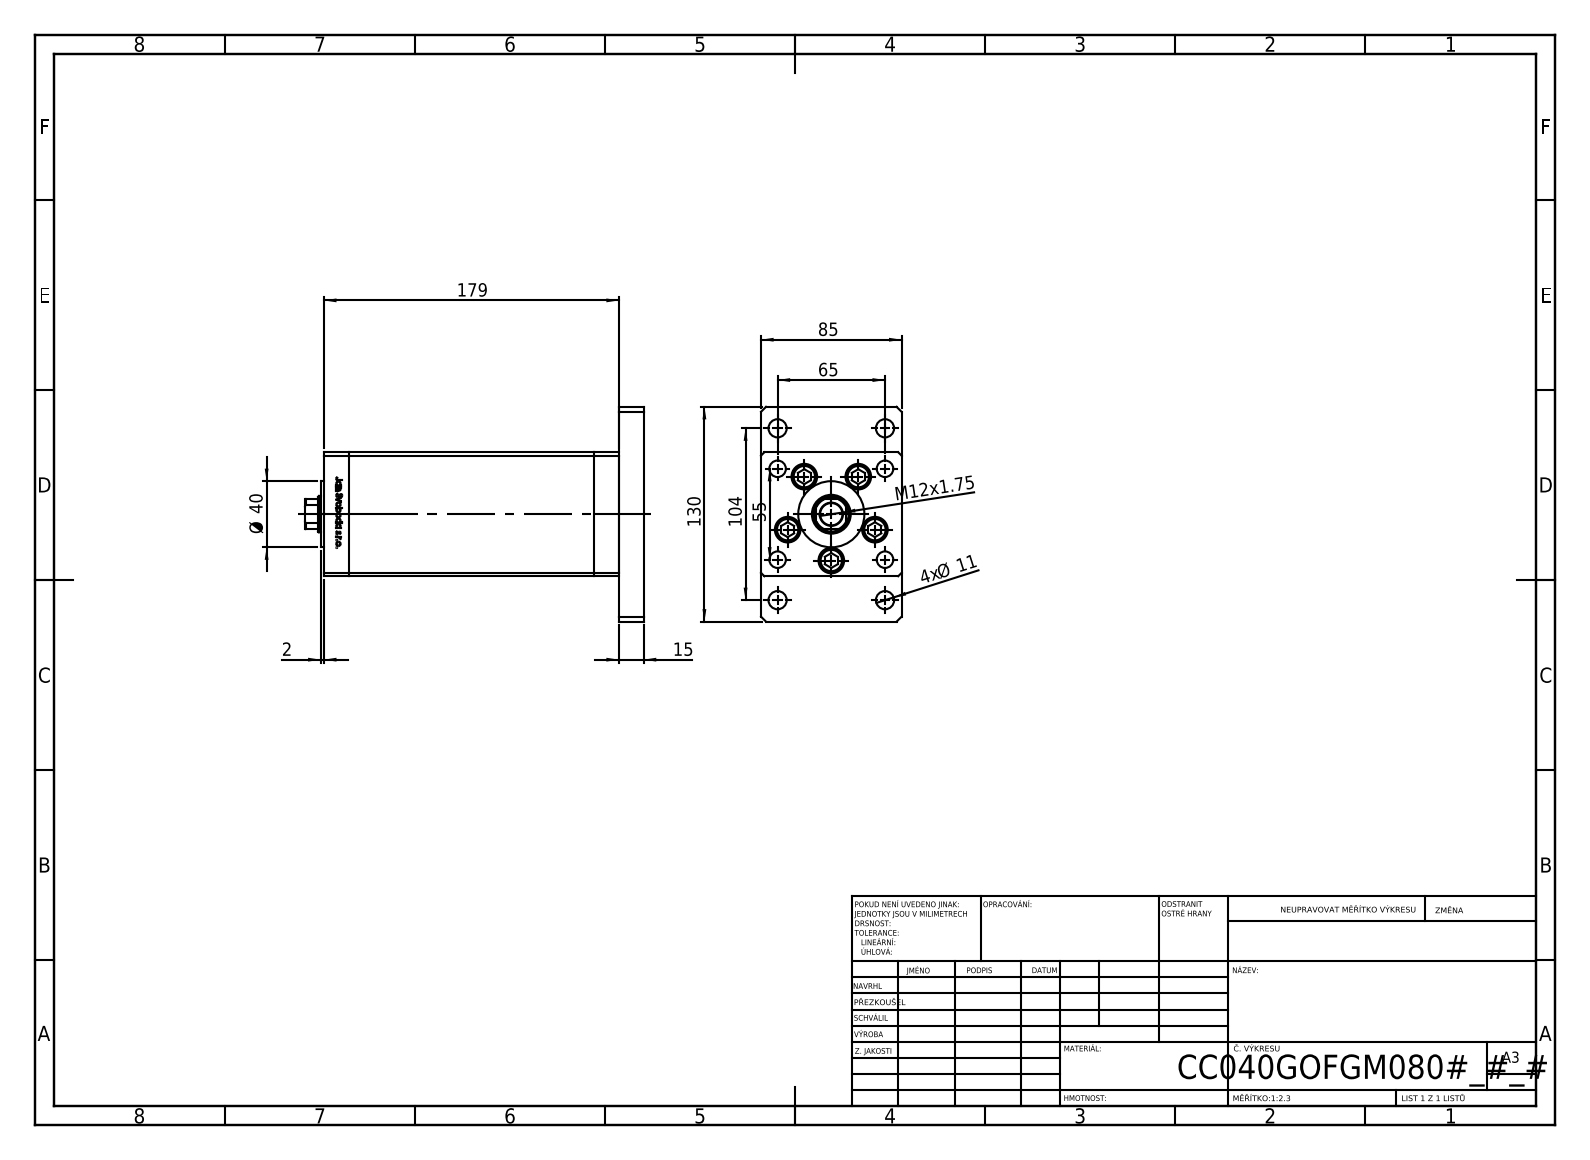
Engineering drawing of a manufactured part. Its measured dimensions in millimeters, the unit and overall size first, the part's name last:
Units: millimetres
Overall size (bounding box): 205 × 130 × 85
Round holes (diameter × count): ⌀10 ×9, ⌀11 ×9, ⌀15.5 ×5, ⌀14.5 ×4, ⌀13.5 ×1, ⌀22 ×1, ⌀23.5 ×1, ⌀56 ×1
Round bosses / shafts (diameter × count): ⌀8 ×9, ⌀14.5 ×5, ⌀40 ×1
Partial cylindrical surfaces — rounded edges, fillets, slot ends (radius × count): R0.93 ×2, R10.5 ×1
Main face-to-face distances: 15, 85, 163.5, 178.5, 75, 148.5, 30, 2, 176.5, 193.5
Hole centre spacings: 28, 24.5, 42.57, 61.32, 65, 69.46, 79.5, 102.69
Volume: 1 162 000 mm³ · Surface area: 196 296 mm²
Bodies: 19 solids, 1301 faces (514 planar, 181 cylindrical, 606 other)
Part name (STEP PRODUCT): V220C_F; V220C_VC_G; V220C_FRONT_G; ALLEN BOLT (+2 more)
STEP written by: SolidWorks 2019 (CONFIG_CONTROL_DESIGN)
